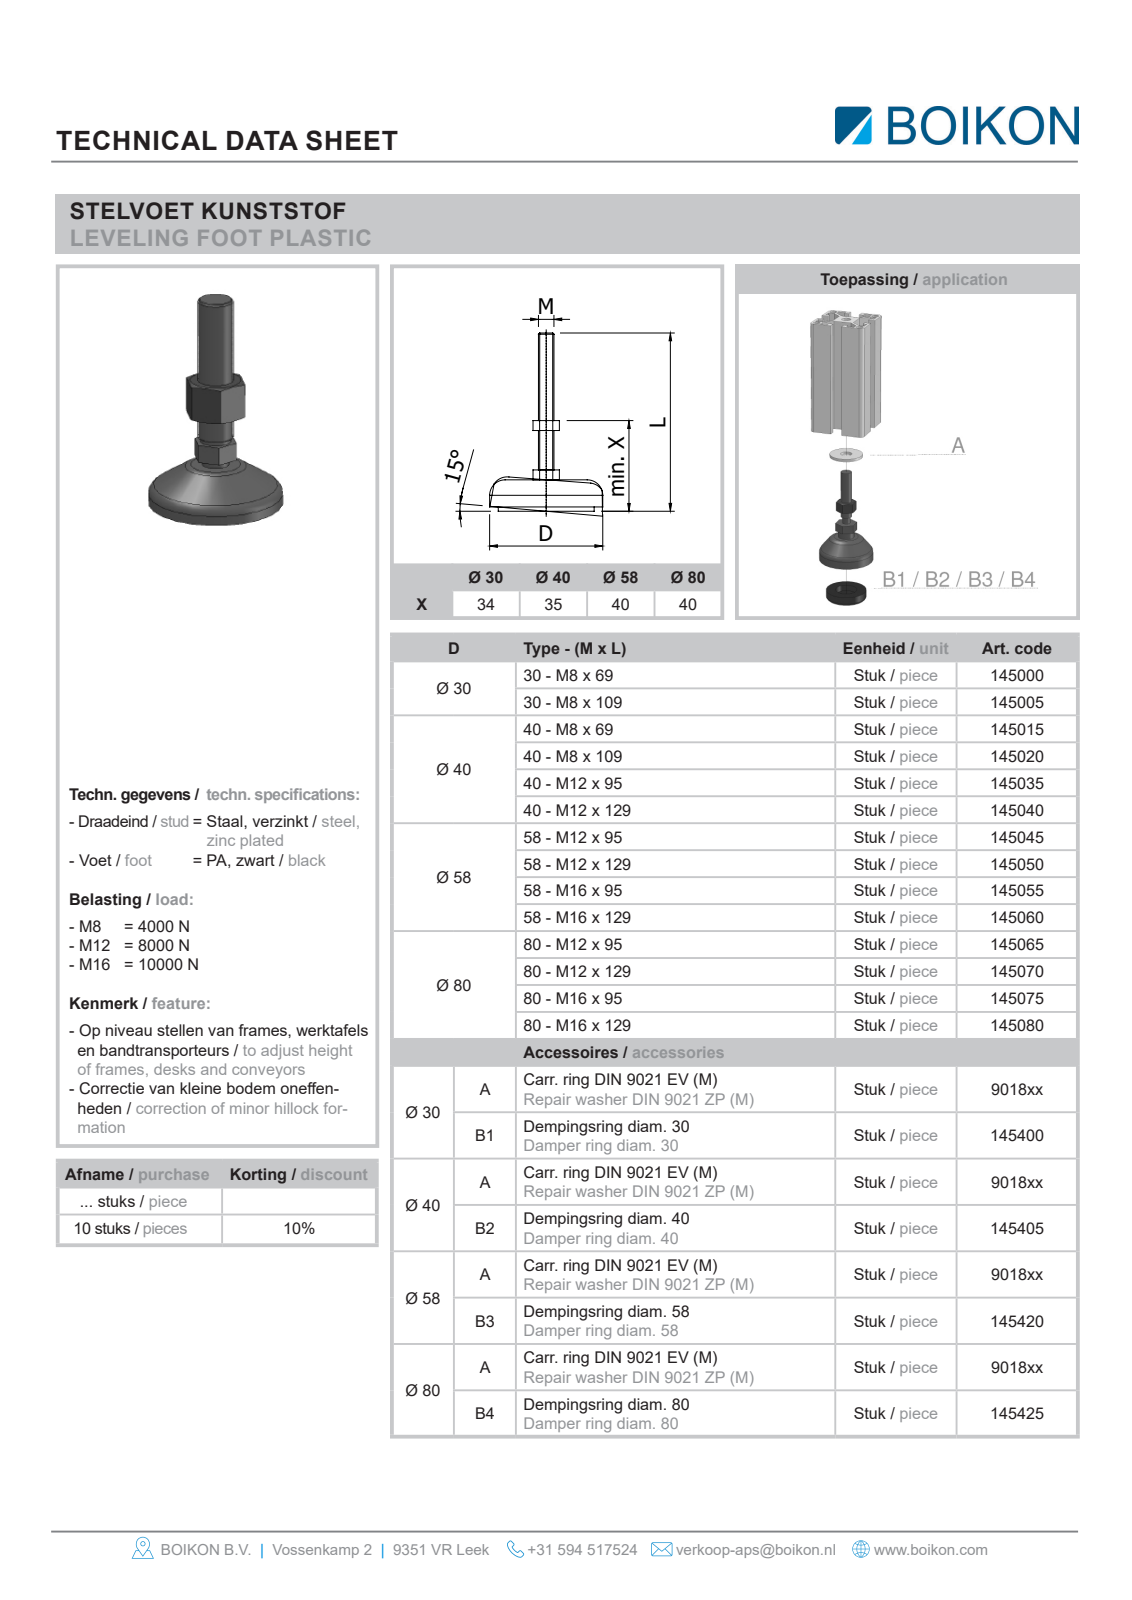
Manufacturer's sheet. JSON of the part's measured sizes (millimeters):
{"part_name": "Root; 145035Stelvoet 40 - M12 x 95, kunststofBOIKON; 901812Carr. ring DIN 9021 EV M12BOIKON0; 145405Dempingsring diam. 40BOIKON0 (+1 more)", "step_written_by": "HiCAD 2013 1802.4 Build 509 (AUTOMOTIVE_DESIGN)", "units": "millimeters", "bodies": {"solids": 4, "faces": 46, "planar": 27, "cylindrical": 11, "other": 8}, "overall_size": [97, 40, 40], "volume_mm3": 32146, "surface_area_mm2": 13756, "round_holes": [[10.11, 1], [13, 1], [16, 1], [33, 1]], "round_bosses_or_shafts": [[40, 1], [37, 1], [30, 1], [15, 1], [12, 1], [10, 1]], "face_to_face_distances": [49.7, 53, 3.3, 2, 18, 7, 56.7, 60, 5, 16]}
